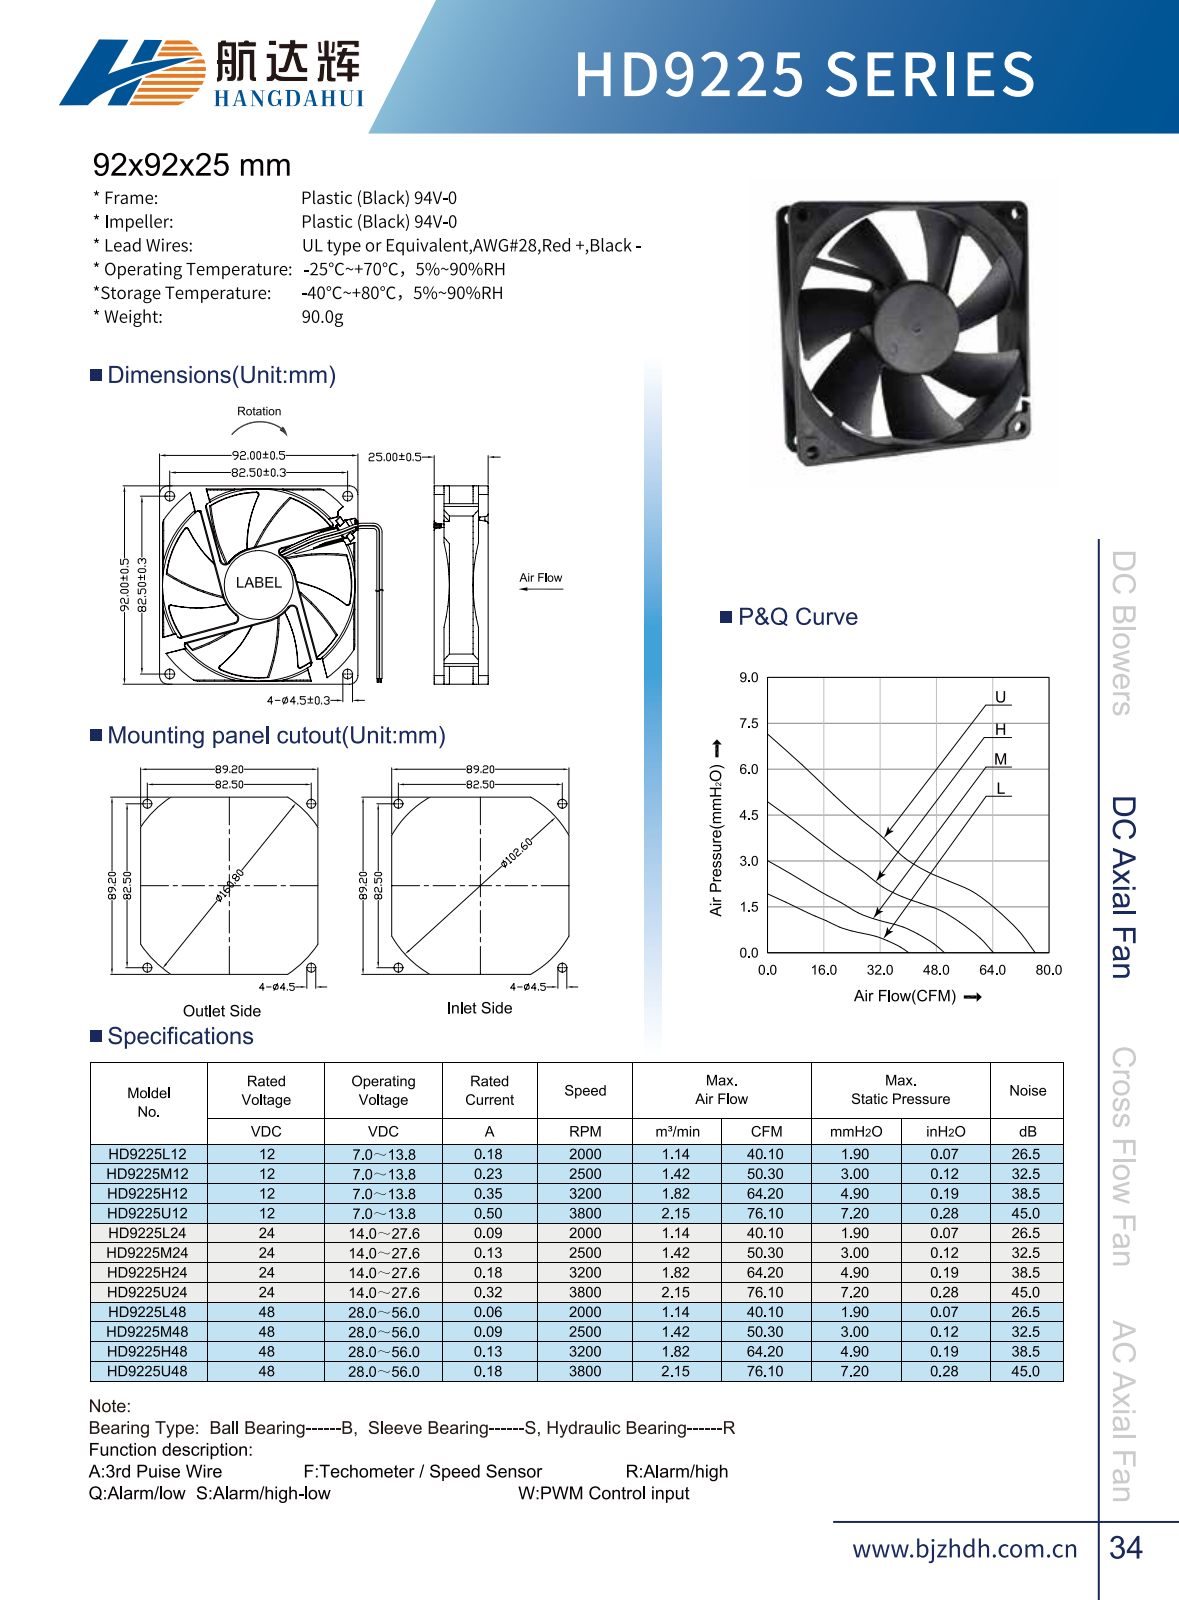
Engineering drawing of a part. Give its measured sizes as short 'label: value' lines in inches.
name: AdmiB7F0ezlq
written by: UGS - NX 4.0 (CONFIG_CONTROL_DESIGN)
unit: in
bodies: 1 solid, 333 faces (95 planar, 96 cylindrical, 142 other)
size: 3.622 × 3.622 × 0.984
volume: 1.757 in³; area: 42.3 in²
holes: 4× ⌀0.177, 1× ⌀3.512
bosses: 1× ⌀3.622, 1× ⌀1.378
rounds: 19× R0.079, 18× R0.02, 16× R0.039, 4× R0.02, 4× R0.03, 4× R0.157, 1× R0.025, 1× R0.039
face distances: 0.177, 3.622, 0.059, 0.055, 3.567, 0.807, 0.748, 0.236, 0.571, 0.63
hole spacings: 2.297, 3.248, 4.593
